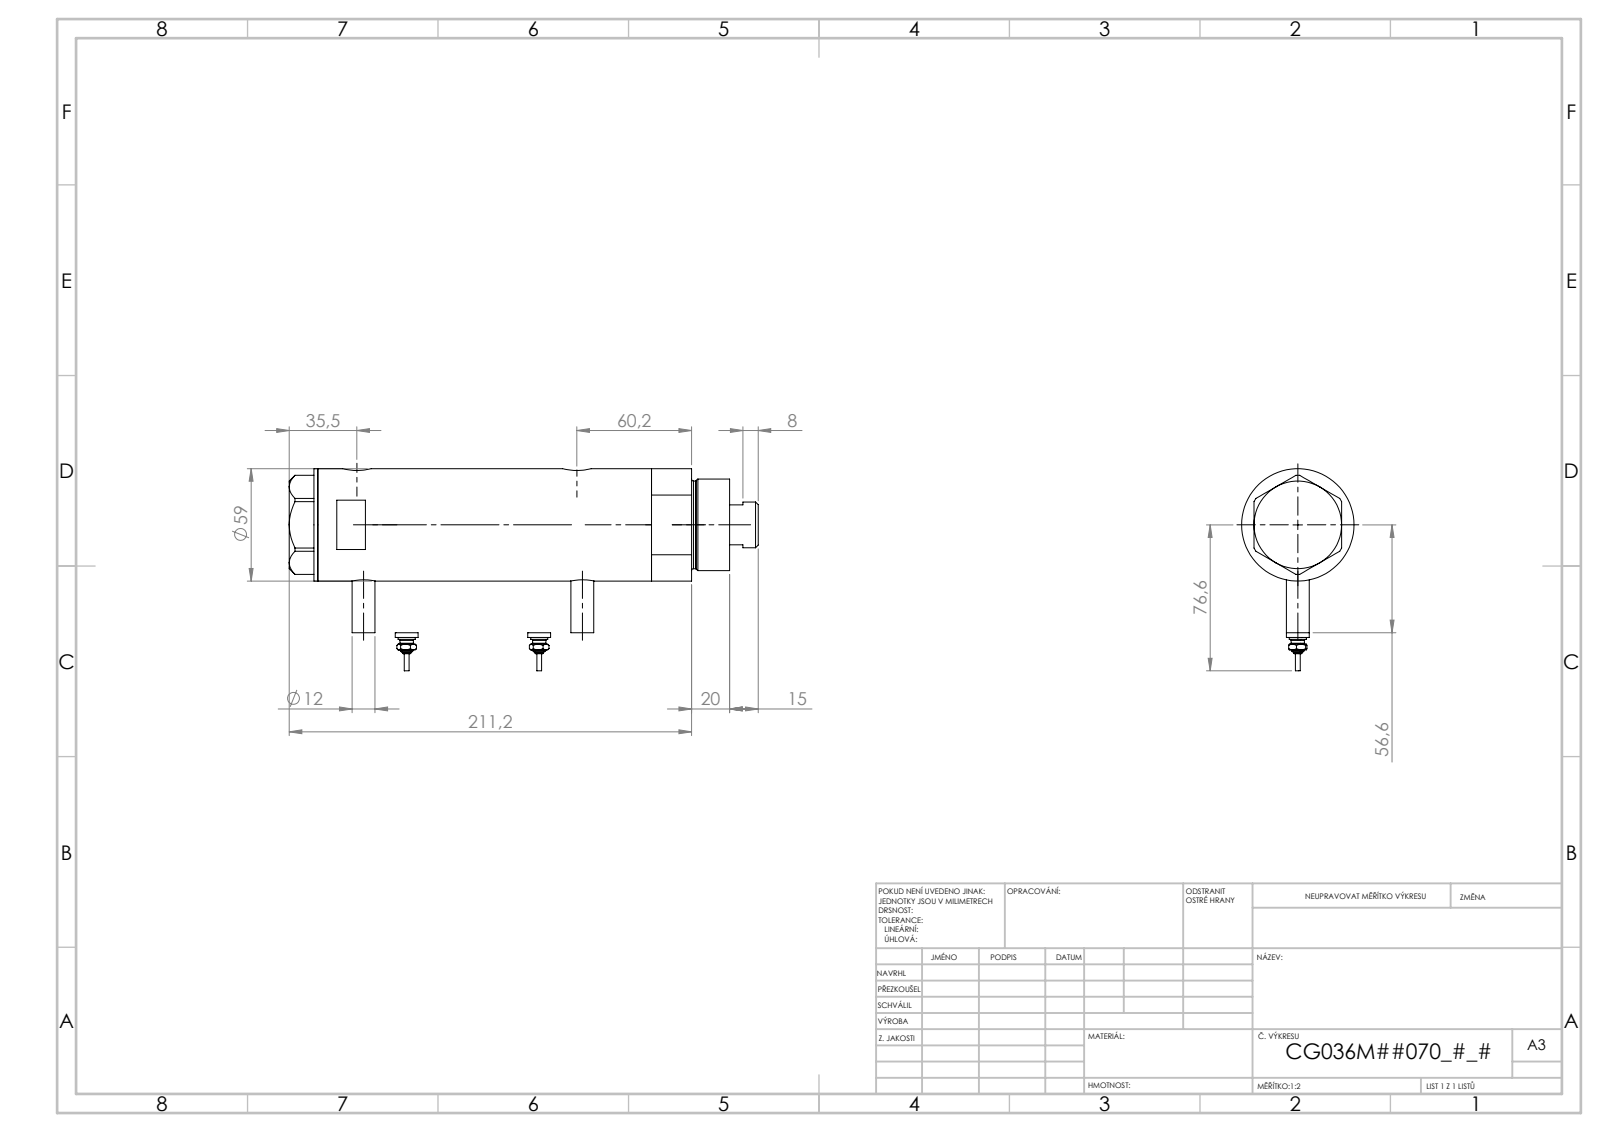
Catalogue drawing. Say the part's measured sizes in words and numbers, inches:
The part is named "V270CG_BACK; V270CG_SWITCH; V270CG_VC; V270CG_FRONT (+1 more)". Its 3-D file was written by "SolidWorks 2019 (CONFIG_CONTROL_DESIGN)". It is 6 solids with 232 faces: 81 planar, 77 cylindrical and 74 other. Overall it measures 9.19 by 3.594 by 2.323 inches. Its volume is 32.25 cubic inches and its surface area 170.9 square inches. Round holes: 2 of diameter 0.197, 2 of diameter 0.383, 2 of diameter 0.492, 2 of diameter 0.591, 1 of diameter 0.335, 1 of diameter 0.984, 1 of diameter 1.043, 1 of diameter 1.417, 1 of diameter 1.575, 1 of diameter 2.047. Round bosses or shafts: 4 of diameter 0.472, 2 of diameter 0.354, 2 of diameter 0.276, 2 of diameter 0.171, 2 of diameter 0.094, 1 of diameter 2.323, 1 of diameter 1.89, 1 of diameter 1.811. The main face-to-face distances are 5.013, 0.925, 4.088, 0.591, 1.516, 5.604, 8.599, 8.009, 7.083, 2.995. The hole center spacings are 0.114, 0.138, 4.022, 4.136, 4.159, 4.274, 0.114, 0.115.
